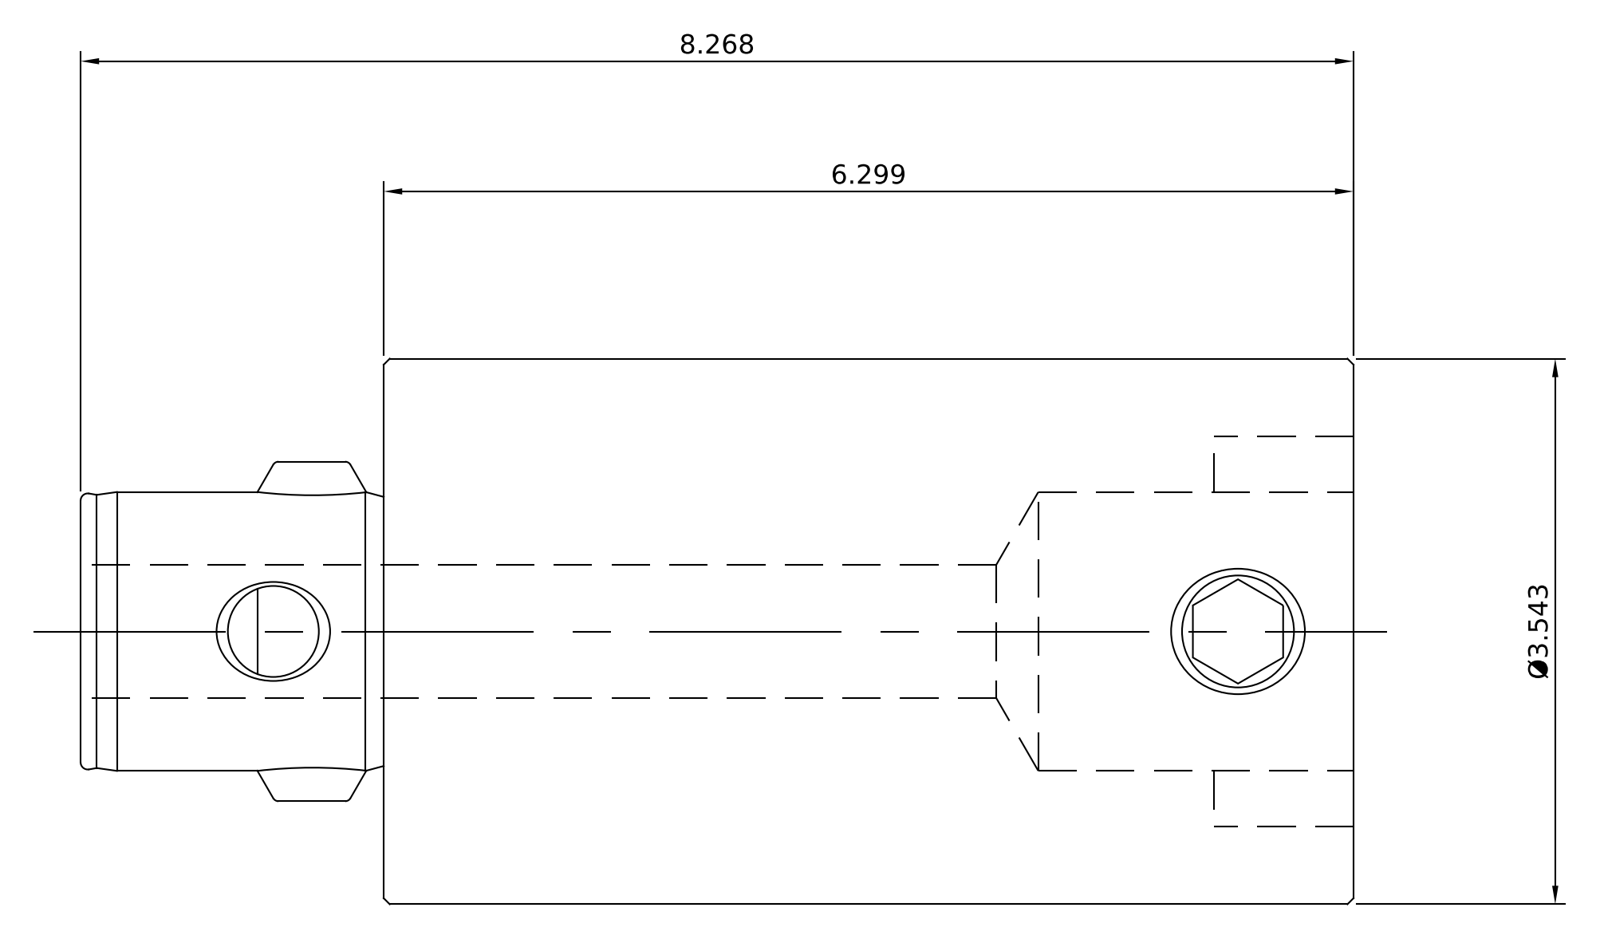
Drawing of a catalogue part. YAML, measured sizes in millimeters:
part_name: "11.331.771_11.331.771; 11.331.771; 10.691.50X_10.691.507; 691-50XRing_10.691.507Ring (+1 more)"
step_written_by: "SolidWorks 2016 (AUTOMOTIVE_DESIGN)"
units: millimeters
bodies: {solids: 4, faces: 142, planar: 39, cylindrical: 47, other: 56}
overall_size: [210, 90, 90]
volume: 921018
surface_area: 93305
round_holes:
  - {diameter: 8, count: 1}
  - {diameter: 15, count: 1}
  - {diameter: 17.5, count: 1}
  - {diameter: 18, count: 1}
  - {diameter: 21, count: 1}
  - {diameter: 22, count: 1}
  - {diameter: 24.7, count: 1}
  - {diameter: 36, count: 1}
  - {diameter: 46, count: 1}
  - {diameter: 47, count: 1}
round_bosses_or_shafts:
  - {diameter: 90, count: 1}
  - {diameter: 89.6, count: 1}
  - {diameter: 20, count: 1}
  - {diameter: 17.9, count: 1}
  - {diameter: 15.9, count: 1}
  - {diameter: 12, count: 1}
partial_cylinders:
  - {radius: 7, count: 2}
  - {radius: 23, count: 1}
face_to_face_distances: [160, 50, 210, 154, 104, 56, 39.14, 188, 138, 34]
hole_center_spacings: [34, 159.15]
